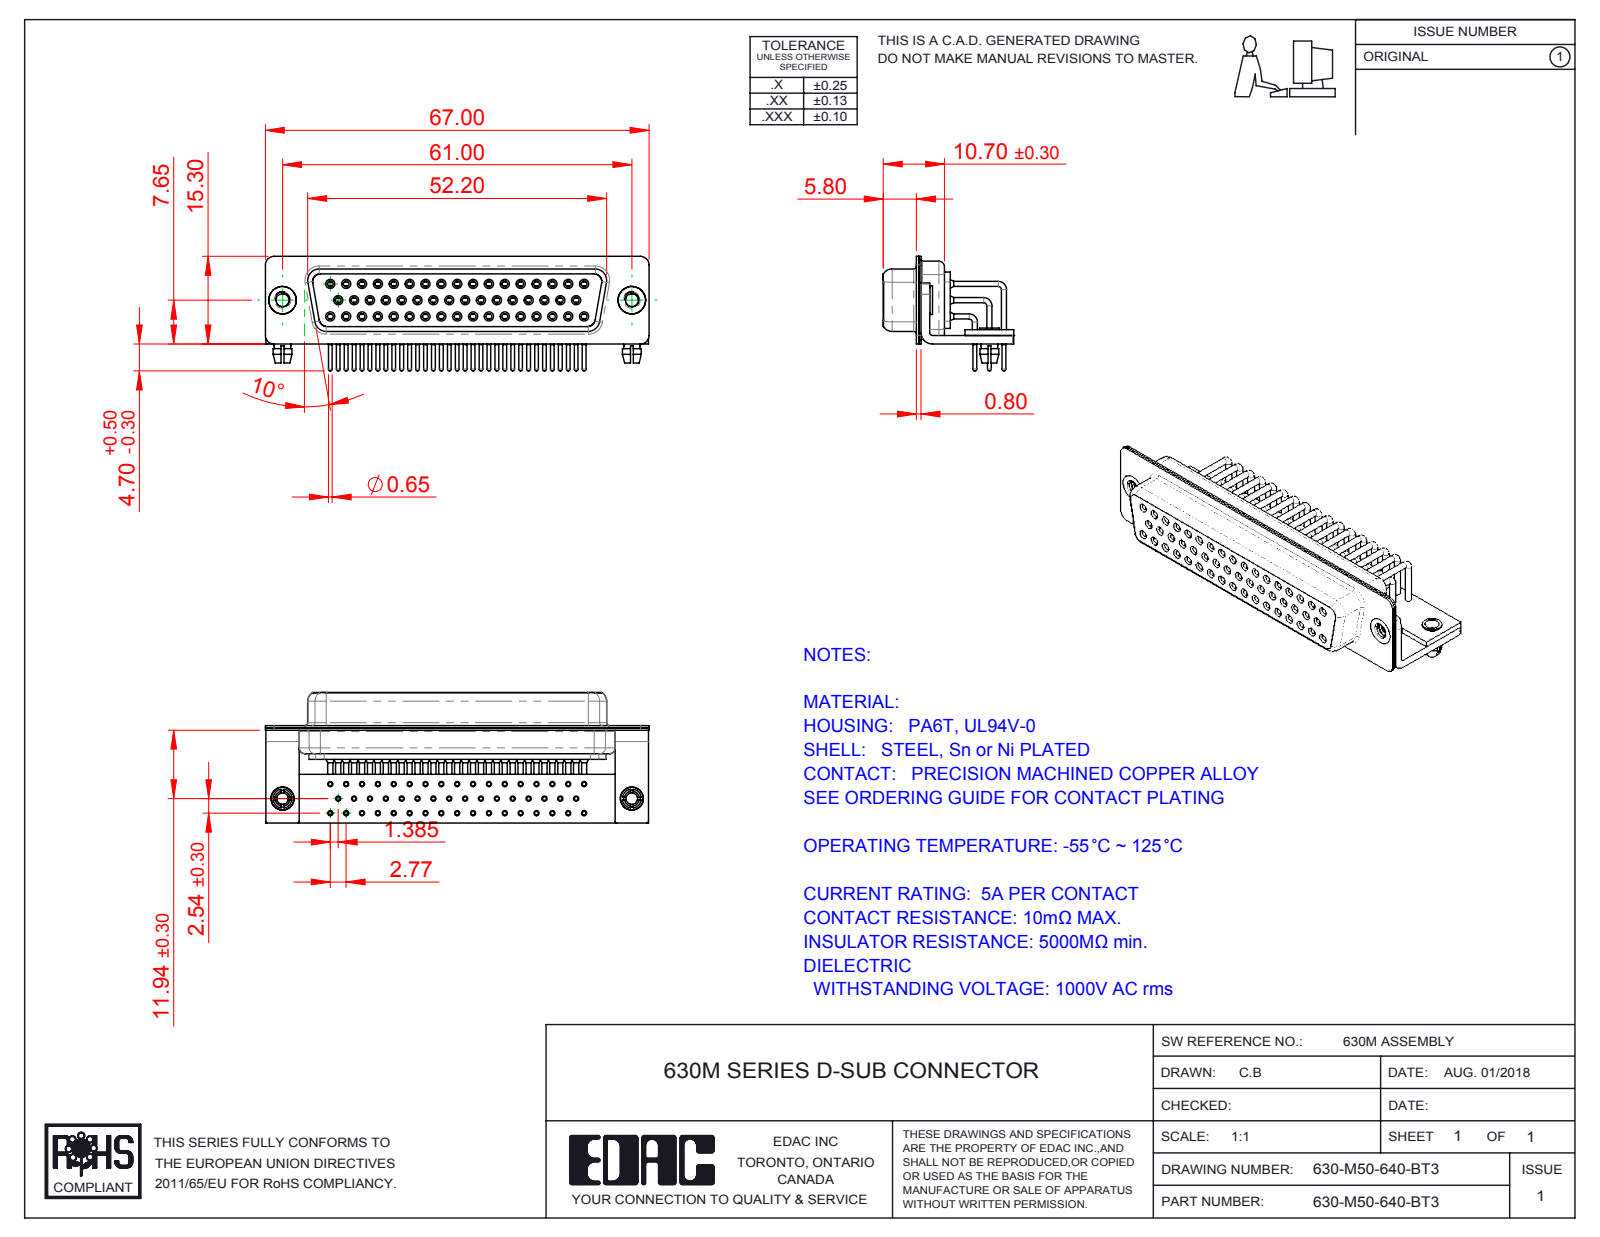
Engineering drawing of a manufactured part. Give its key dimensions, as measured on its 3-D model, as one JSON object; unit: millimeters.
{"part_name": "630M Stabilizer Board_50 Contacts; 630M Stabilizer Bracket_50 Contacts; 630-M50-640-BT3; 630M 4-40 Threaded Rivet_Stabilizer (+7 more)", "step_written_by": "SolidWorks 2016 (CONFIG_CONTROL_DESIGN)", "units": "millimeters", "bodies": {"solids": 60, "faces": 3171, "planar": 891, "cylindrical": 1441, "other": 839}, "overall_size": [67, 22.8, 20], "volume_mm3": 7910, "surface_area_mm2": 18844, "round_holes": [[2, 52], [0.9, 50], [1, 50], [1.1, 50], [1.7, 50], [1.8, 50], [2.26, 2], [2.5, 2], [3.2, 2], [4, 2], [4.8, 2]], "round_bosses_or_shafts": [[0.9, 59], [1.6, 50], [1.5, 50], [0.65, 50], [5, 2], [4.9, 2], [4, 2], [3.4, 2]], "partial_cylinders_radius": [[0.25, 16], [1.5, 16], [2, 13], [1.35, 8], [1.6, 8], [0.5, 5], [0.6, 4], [0.65, 4]], "face_to_face_distances": [0.4, 1, 2.2, 0.85, 1.35, 11.85, 12.25, 5.8, 5.9, 0.8], "hole_center_spacings": [2.77, 5.54, 8.31, 11.08, 13.85, 16.62, 3.16, 19.39]}
